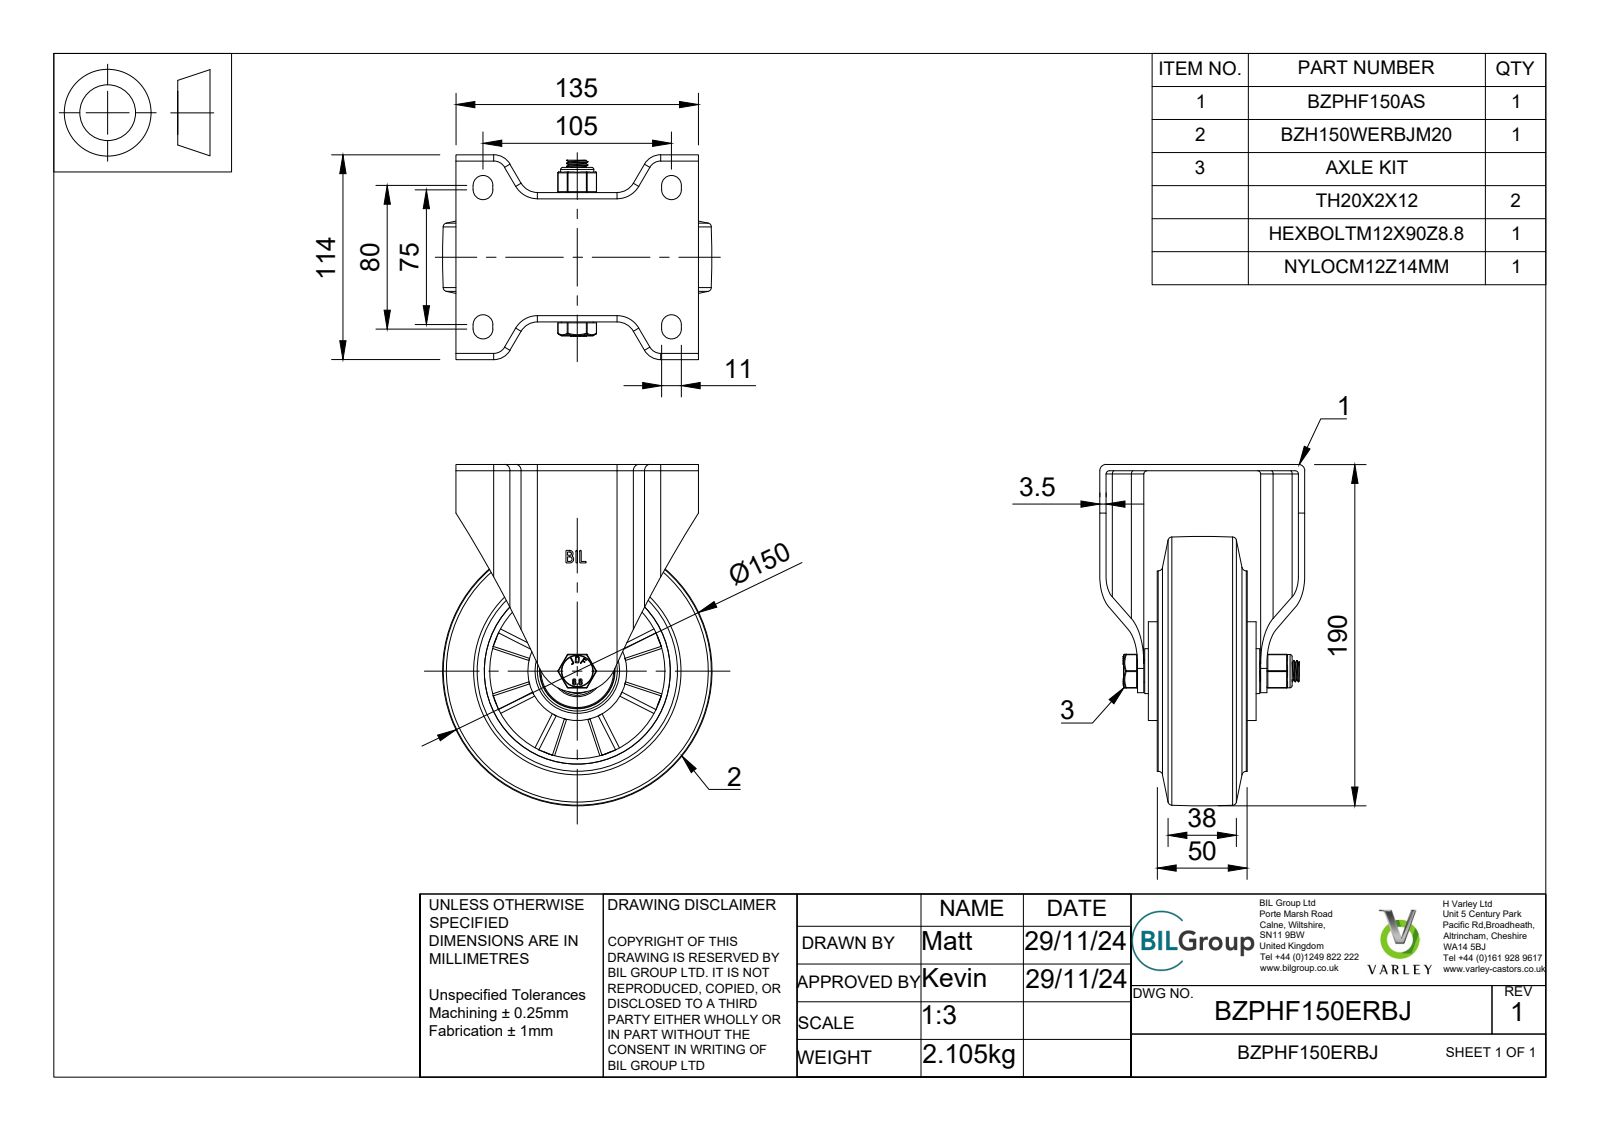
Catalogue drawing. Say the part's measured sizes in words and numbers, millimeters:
The part is named "BZPHF150ERBJ v3; BZPHF150AS - 65 v1; ZINC PLATED, PRESSED STEEL BRACKET (1); BZH150WERBJM20 v1 (+8 more)". Its 3-D file was written by "Autodesk Translation Framework v13.20.0.188 (AP242_MANAGED_MODEL_BASED_3D_ENGINEERING_MIM_LF)". It is 35 solids with 1492 faces: 661 planar, 297 cylindrical and 534 other. Overall it measures 190 by 150 by 114 millimeters. Its volume is 711 681 cubic millimeters and its surface area 254 658 square millimeters. Round holes: 1 of diameter 12, 1 of diameter 12.1, 1 of diameter 12.2, 1 of diameter 14, 1 of diameter 20, 1 of diameter 28.5, 1 of diameter 32, 1 of diameter 41.5, 1 of diameter 42, 1 of diameter 44, 1 of diameter 47, 1 of diameter 97.5. Round bosses or shafts: 1 of diameter 111.5, 1 of diameter 55, 1 of diameter 40.5, 1 of diameter 40, 1 of diameter 29, 1 of diameter 27, 1 of diameter 25, 1 of diameter 19.8. Partial cylindrical surfaces (rounded edges, fillets, slot ends): 20 of radius 0.5, 12 of radius 4, 12 of radius 6, 8 of radius 1.75, 8 of radius 3.5, 8 of radius 5.5, 8 of radius 10.5, 4 of radius 0.47. The main face-to-face distances are 3.5, 68.5, 11, 49, 21, 89.5, 6, 2.5, 13.5, 55.
